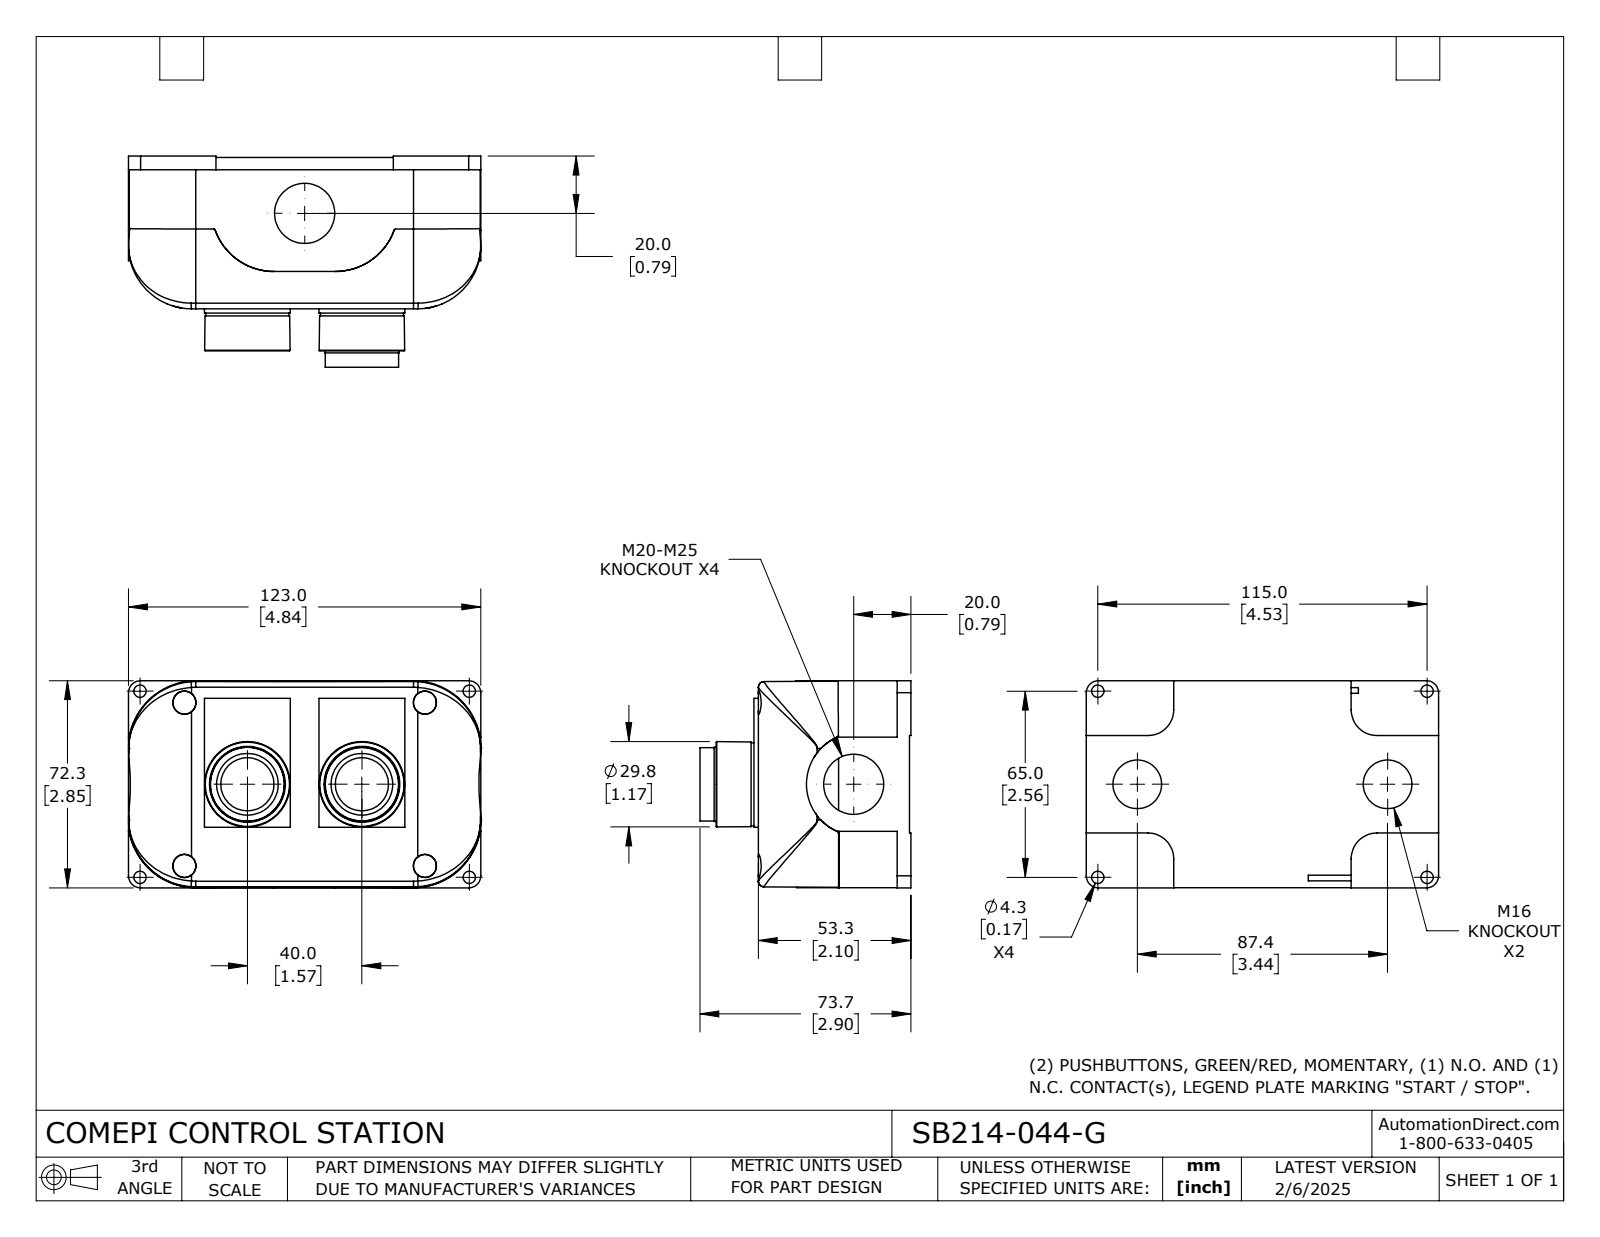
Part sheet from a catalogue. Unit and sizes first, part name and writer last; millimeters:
Units: millimetres
Overall size (bounding box): 123 × 73.7 × 72.3
Round holes (diameter × count): ⌀4.3 ×4, ⌀13.5 ×2, ⌀17 ×2, ⌀21 ×2, ⌀21.7 ×2, ⌀22.5 ×2
Round bosses / shafts (diameter × count): ⌀29 ×2, ⌀19 ×2, ⌀16 ×2, ⌀15.6 ×2, ⌀25.9 ×1, ⌀25.8 ×1, ⌀25.6 ×1
Partial cylindrical surfaces — rounded edges, fillets, slot ends (radius × count): R0.3 ×4, R0.9 ×4, R2 ×4, R4 ×4, R9 ×4, R9.7 ×4, R22 ×4, R23.6 ×4
Main face-to-face distances: 52.8, 2.5, 50.3, 28, 24.8, 22.3, 3, 54.8, 1.5, 54.3
Hole centre spacings: 35.3, 49.6, 84, 106.3, 23.7, 63.7, 65, 115
Volume: 269 900 mm³ · Surface area: 84 770 mm²
Bodies: 10 solids, 454 faces (204 planar, 114 cylindrical, 136 other)
Part name (STEP PRODUCT): SB214-044-G
STEP written by: SolidWorks 2024 (CONFIG_CONTROL_DESIGN)
